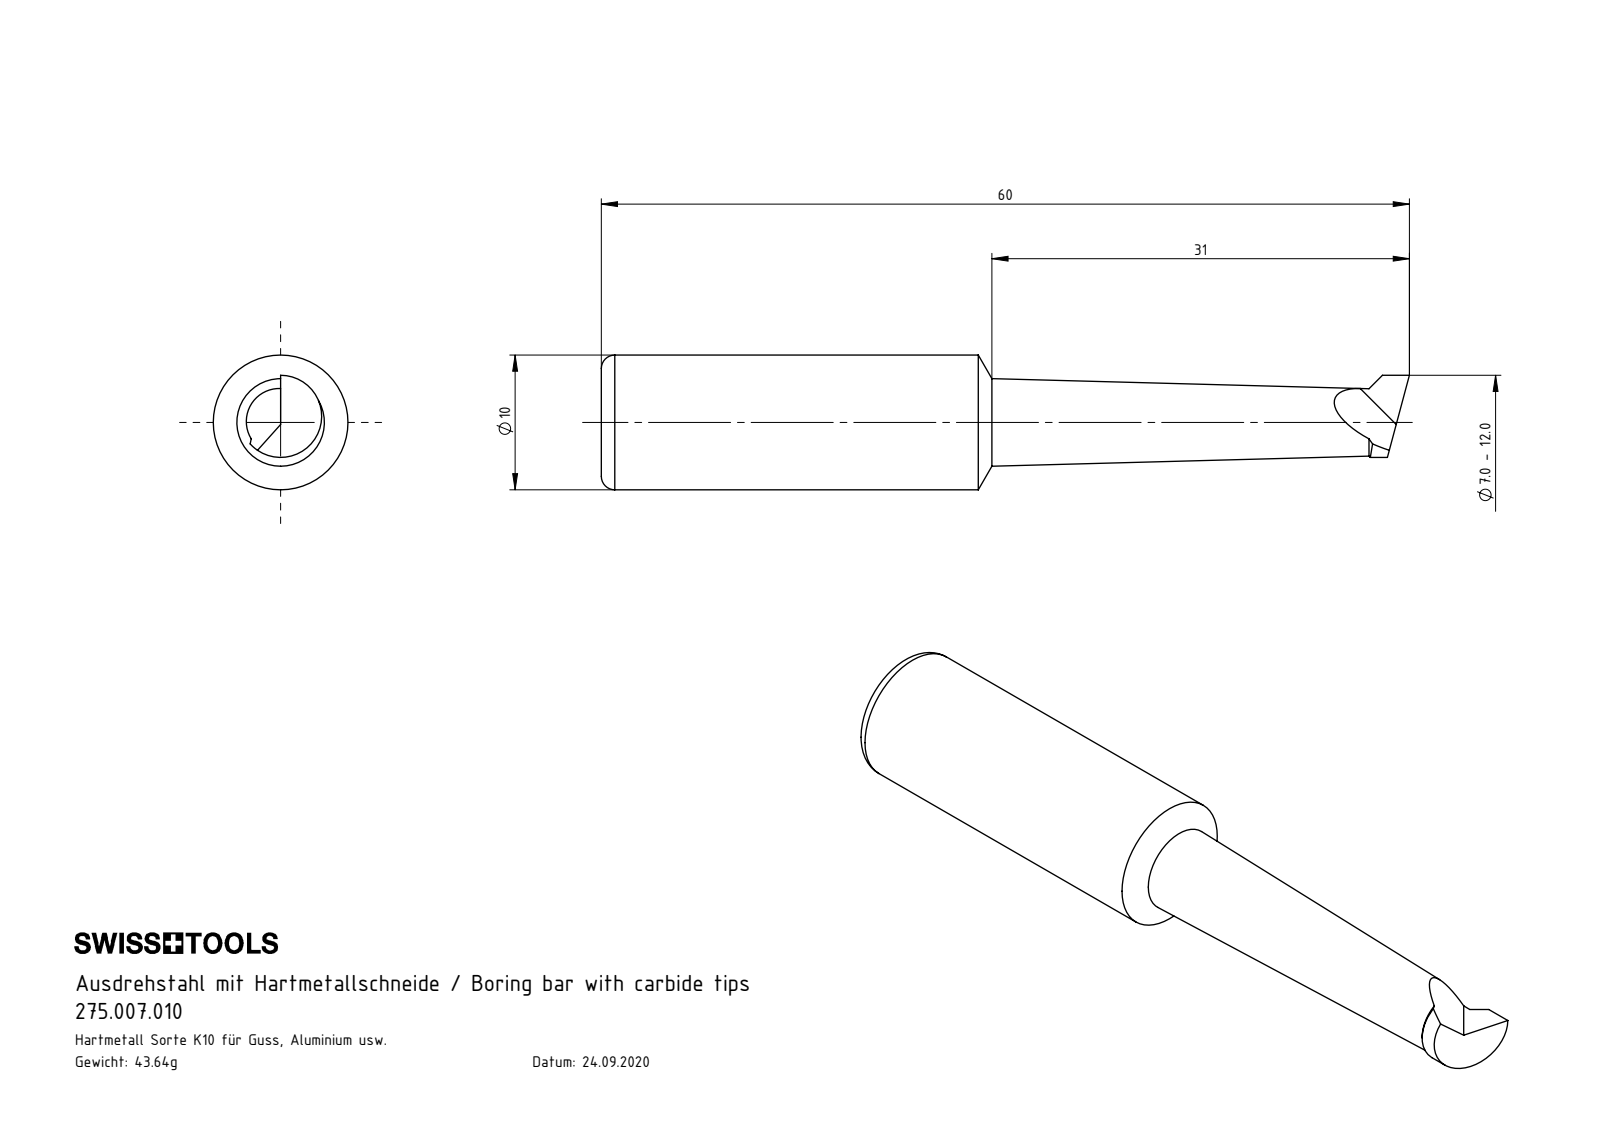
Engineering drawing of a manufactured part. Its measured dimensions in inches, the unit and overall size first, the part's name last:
Units: inches
Overall size (bounding box): 2.362 × 0.394 × 0.394
Round bosses / shafts (diameter × count): ⌀0.394 ×1
Partial cylindrical surfaces — rounded edges, fillets, slot ends (radius × count): R0.031 ×1
Volume: 0.189 in³ · Surface area: 2.477 in²
Bodies: 1 solid, 27 faces (3 planar, 3 cylindrical, 21 other)
Part name (STEP PRODUCT): U10-B07.001.031
STEP written by: SolidWorks 2017 (CONFIG_CONTROL_DESIGN)
